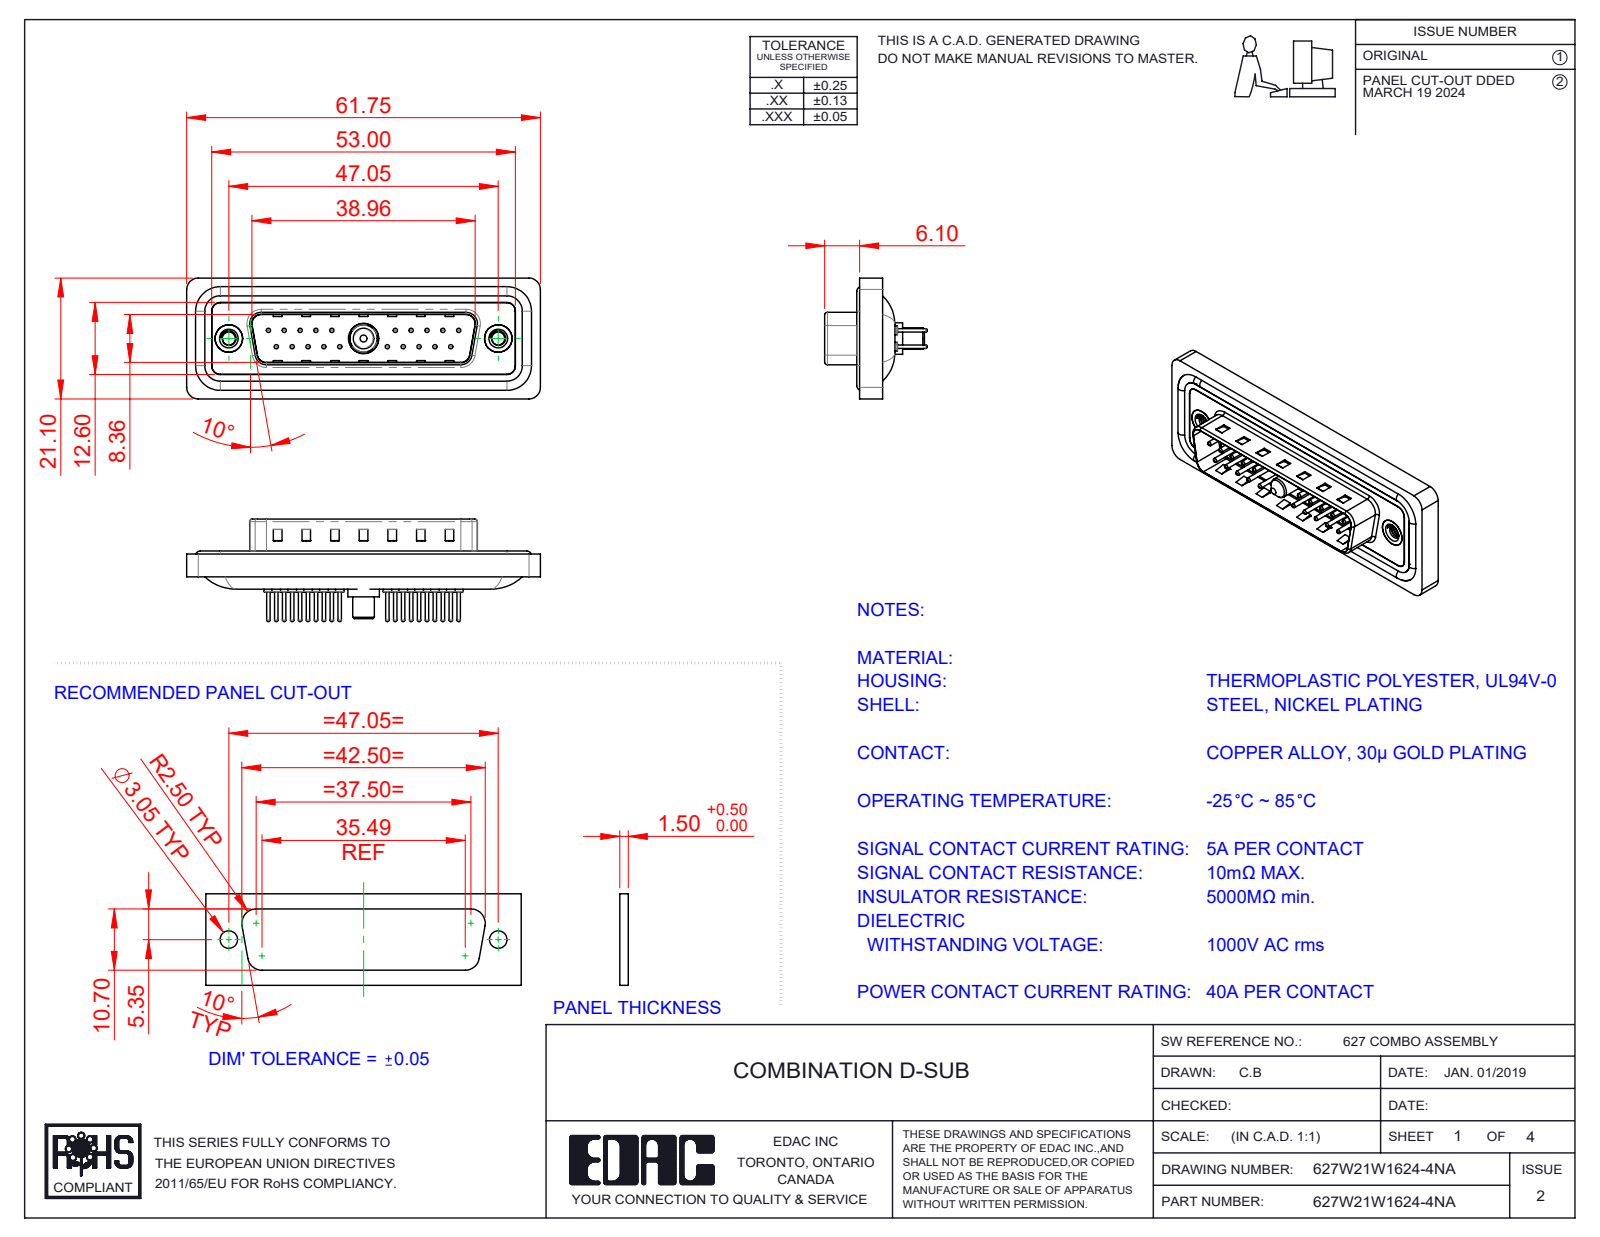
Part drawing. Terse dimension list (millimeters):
name: 627Combo Contact Row 1_24; 627Combo Contact Row 2_24; 627Combo Shell Rear_25 Contacts; 627W21W1624-4NA (+5 more)
written by: SolidWorks 2023 (CONFIG_CONTROL_DESIGN)
unit: mm
bodies: 29 solids, 1260 faces (359 planar, 489 cylindrical, 412 other)
size: 61.75 × 21.1 × 17.9
volume: 7 218 mm³; area: 11 962 mm²
holes: 20× ⌀0.75, 20× ⌀1.6, 20× ⌀2, 2× ⌀2.26, 2× ⌀4, 2× ⌀4.8, 2× ⌀5, 1× ⌀4.85, 1× ⌀5.3
bosses: 20× ⌀1.5, 20× ⌀0.6, 4× ⌀1.6, 2× ⌀4.9, 1× ⌀5.5, 1× ⌀5.2, 1× ⌀4.75, 1× ⌀3.75
rounds: 22× R1.5, 18× R2, 8× R0.5, 8× R1.6, 4× R0.25, 4× R0.6, 4× R0.65, 4× R0.9
face distances: 0.4, 1.5, 1.1, 1.6, 0.5, 3.1, 2.9, 4.1, 0.82, 9.58
hole spacings: 3.16, 2.77, 5.54, 8.31, 5.04, 19.39, 20.97, 22.16
